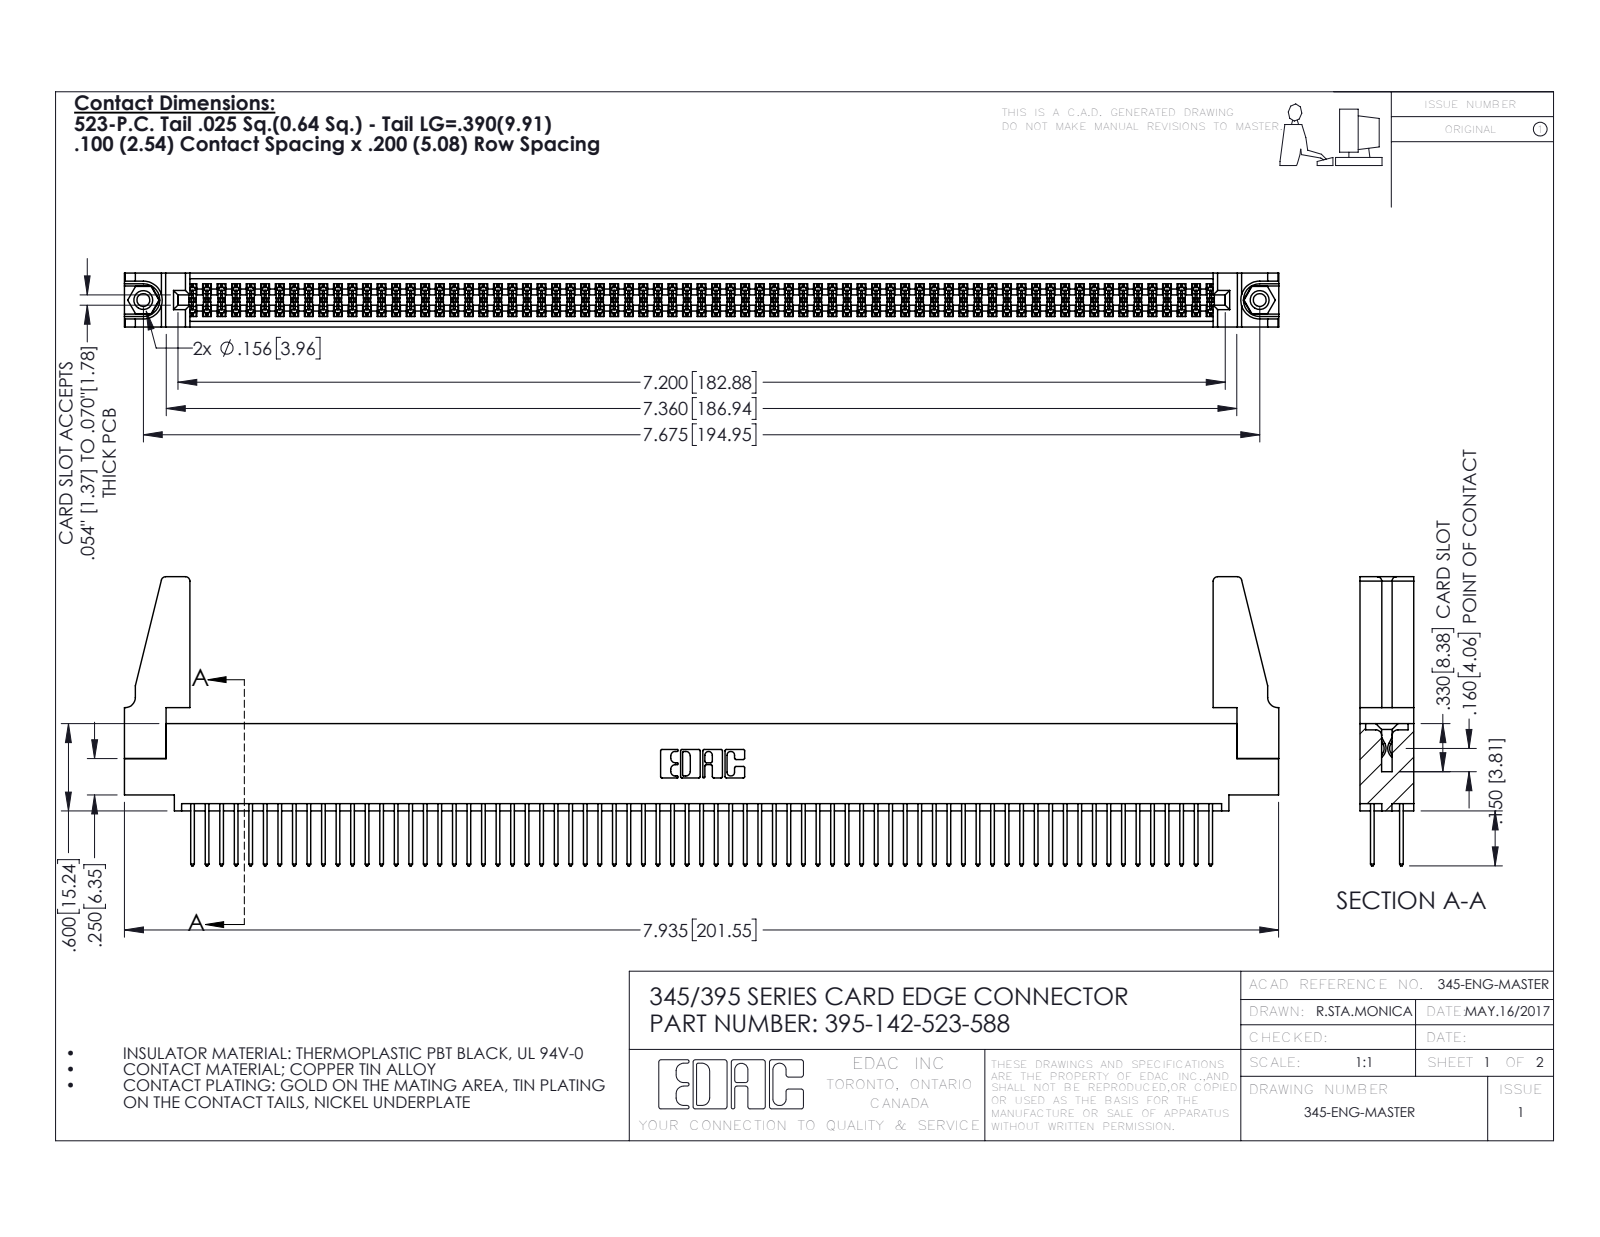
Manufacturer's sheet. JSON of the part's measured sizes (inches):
{"part_name": "345-220-078_345-220-088; 395-142-523-588; 345-292-001_345-293-123; 345-250-001_345-250-001-102 (+1 more)", "step_written_by": "SolidWorks 2016 (CONFIG_CONTROL_DESIGN)", "units": "inches", "bodies": {"solids": 147, "faces": 7354, "planar": 4842, "cylindrical": 2496, "other": 16}, "overall_size": [7.936, 1.987, 0.37], "volume_in3": 1.423, "surface_area_in2": 53.86, "round_holes": [[0.089, 2], [0.125, 2], [0.156, 2], [0.064, 1]], "round_bosses_or_shafts": [[0.155, 2]], "partial_cylinders_radius": [[0.006, 213], [0.01, 142], [0.01, 22], [0.03, 8], [0.007, 6], [0.031, 6], [0.026, 3], [0.014, 2]], "face_to_face_distances": [0.072, 0.298, 0.098, 0.272, 0.025, 0.2, 0.37, 0.225, 0.175, 0.149], "hole_center_spacings": [0.27, 7.439, 7.675]}
